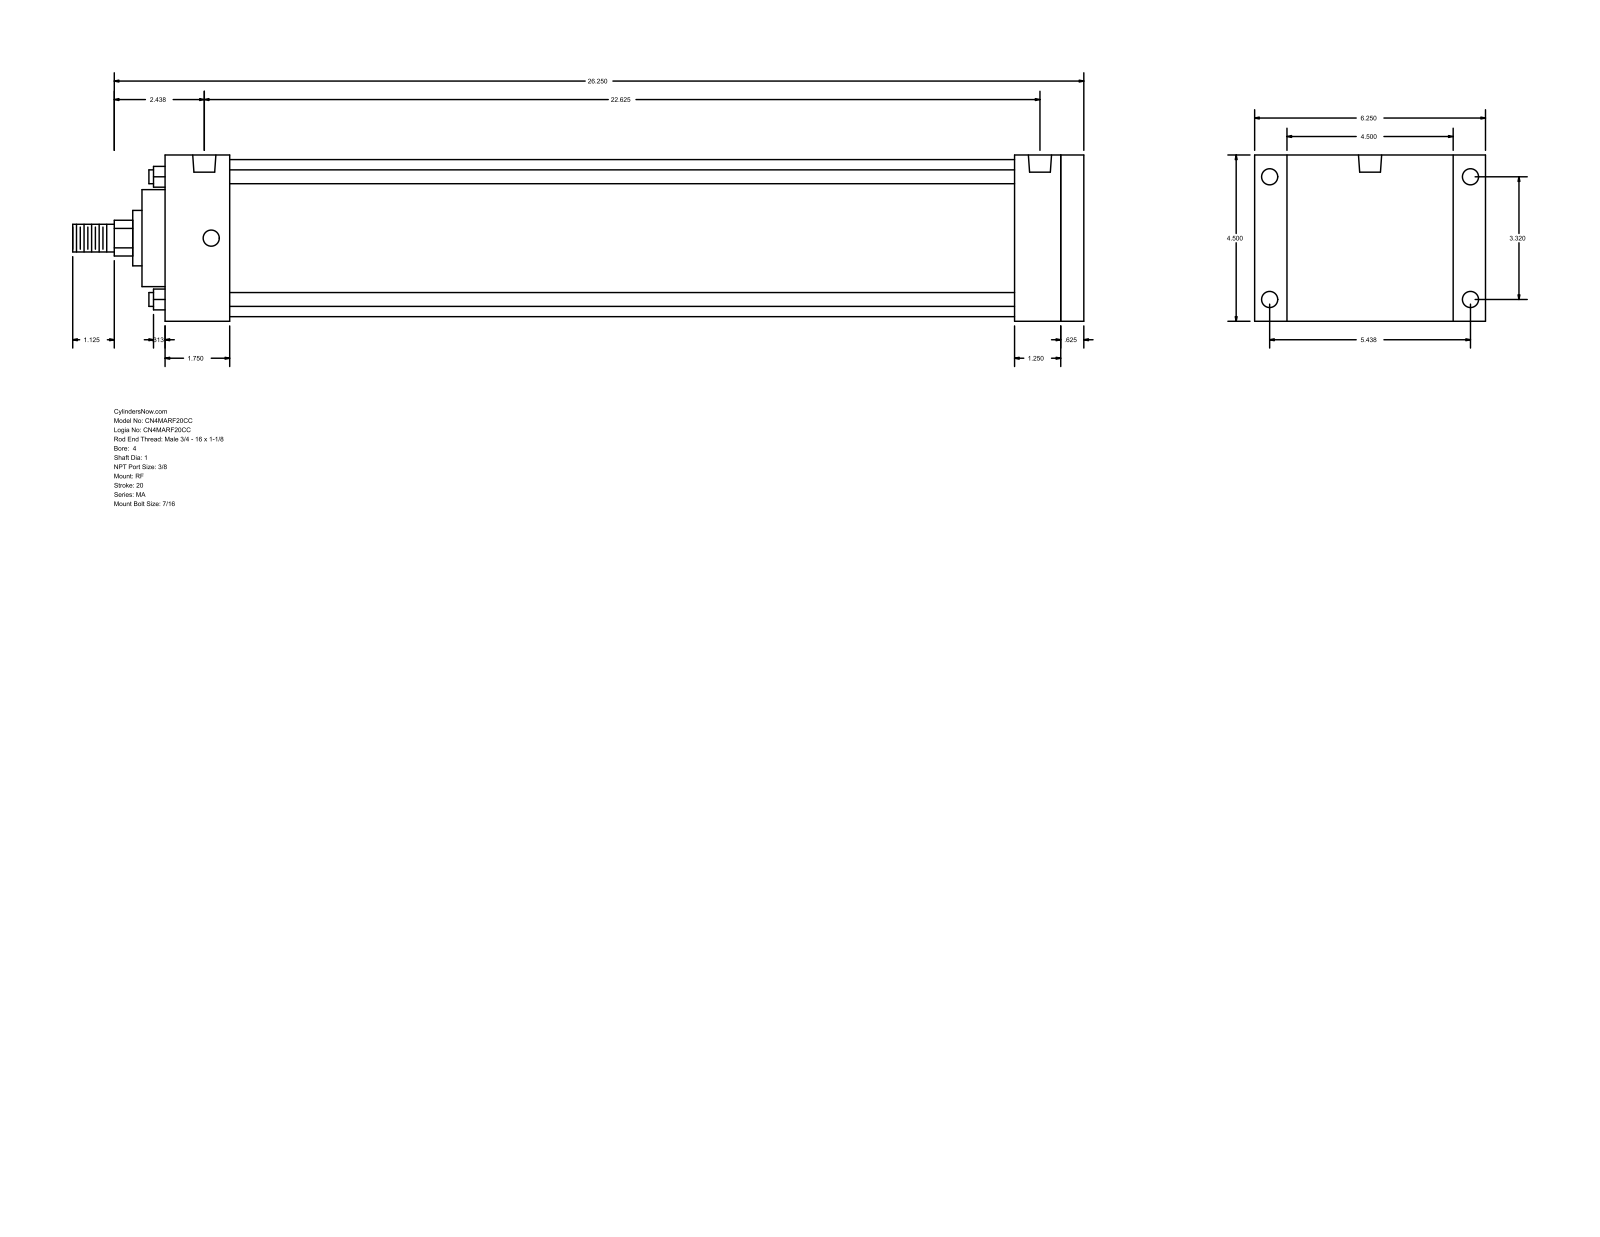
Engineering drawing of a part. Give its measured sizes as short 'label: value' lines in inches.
name: MA_RF__0400_1
written by: GSSL Pune (CONFIG_CONTROL_DESIGN)
unit: in
bodies: 0 solids, 94 faces (65 planar, 29 cylindrical, 0 other)
size: 27.375 × 6.25 × 4.5
holes: 8× ⌀0.437, 2× ⌀0.627
bosses: 4× ⌀0.375, 1× ⌀4.25, 1× ⌀2.625, 1× ⌀1.5, 1× ⌀1, 1× ⌀0.75
rounds: 1× R0.484
face distances: 4.5, 24.875, 0.625, 24.25, 0.875, 5.375, 23, 1.25, 1.875, 1.75
hole spacings: 0.187, 3.32, 5.438, 6.371, 22.25, 22.438, 22.625
